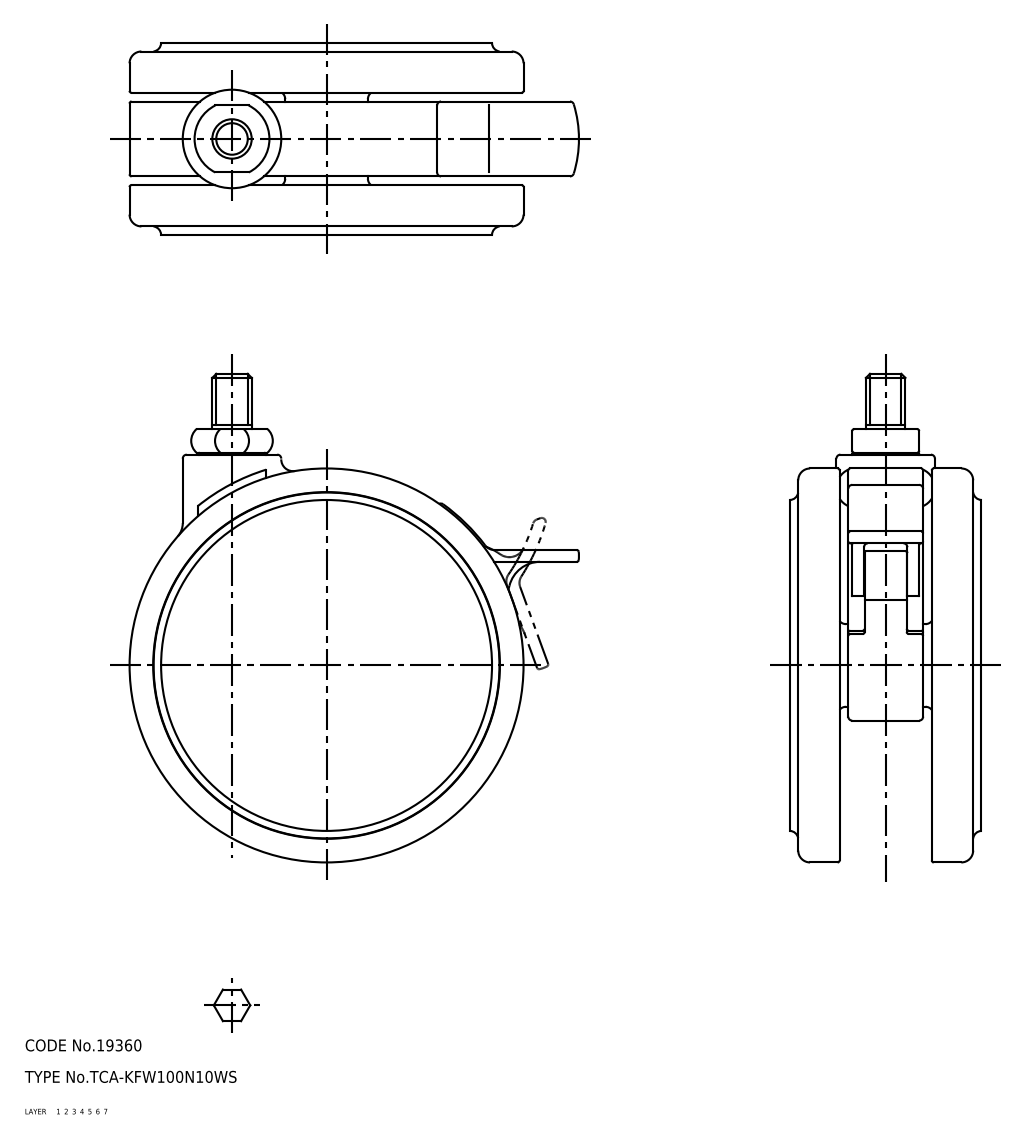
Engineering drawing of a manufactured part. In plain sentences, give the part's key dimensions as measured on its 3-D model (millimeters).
The part is named "caster; TCA-KFW100N10WS". Its 3-D file was written by "SolidWorks 2015 (AUTOMOTIVE_DESIGN)". It is 1 solid with 1520 faces: 528 planar, 654 cylindrical and 338 other. Overall it measures 124 by 114.07 by 48.6 millimeters. Its volume is 185 082 cubic millimeters and its surface area 95 590 square millimeters. Round holes: 1 of diameter 2.4, 1 of diameter 3, 1 of diameter 3.3, 1 of diameter 3.6, 1 of diameter 5.8, 1 of diameter 6.1, 1 of diameter 8.07, 1 of diameter 9, 1 of diameter 9.3, 1 of diameter 10.7, 1 of diameter 12.3, 1 of diameter 13. Round bosses or shafts: 1 of diameter 100, 1 of diameter 87.8, 1 of diameter 25, 1 of diameter 22, 1 of diameter 20, 1 of diameter 17, 1 of diameter 10.5, 1 of diameter 10. Partial cylindrical surfaces (rounded edges, fillets, slot ends): 63 of radius 0.5, 61 of radius 1, 21 of radius 1.5, 18 of radius 0.2, 17 of radius 0.3, 16 of radius 2, 7 of radius 3, 2 of radius 0.7. The main face-to-face distances are 1.8, 45, 46.8, 3.6, 43.2, 12.6, 32.4, 9, 36, 10.8. The hole center spacings are 21.4, 29.97, 43.99.
